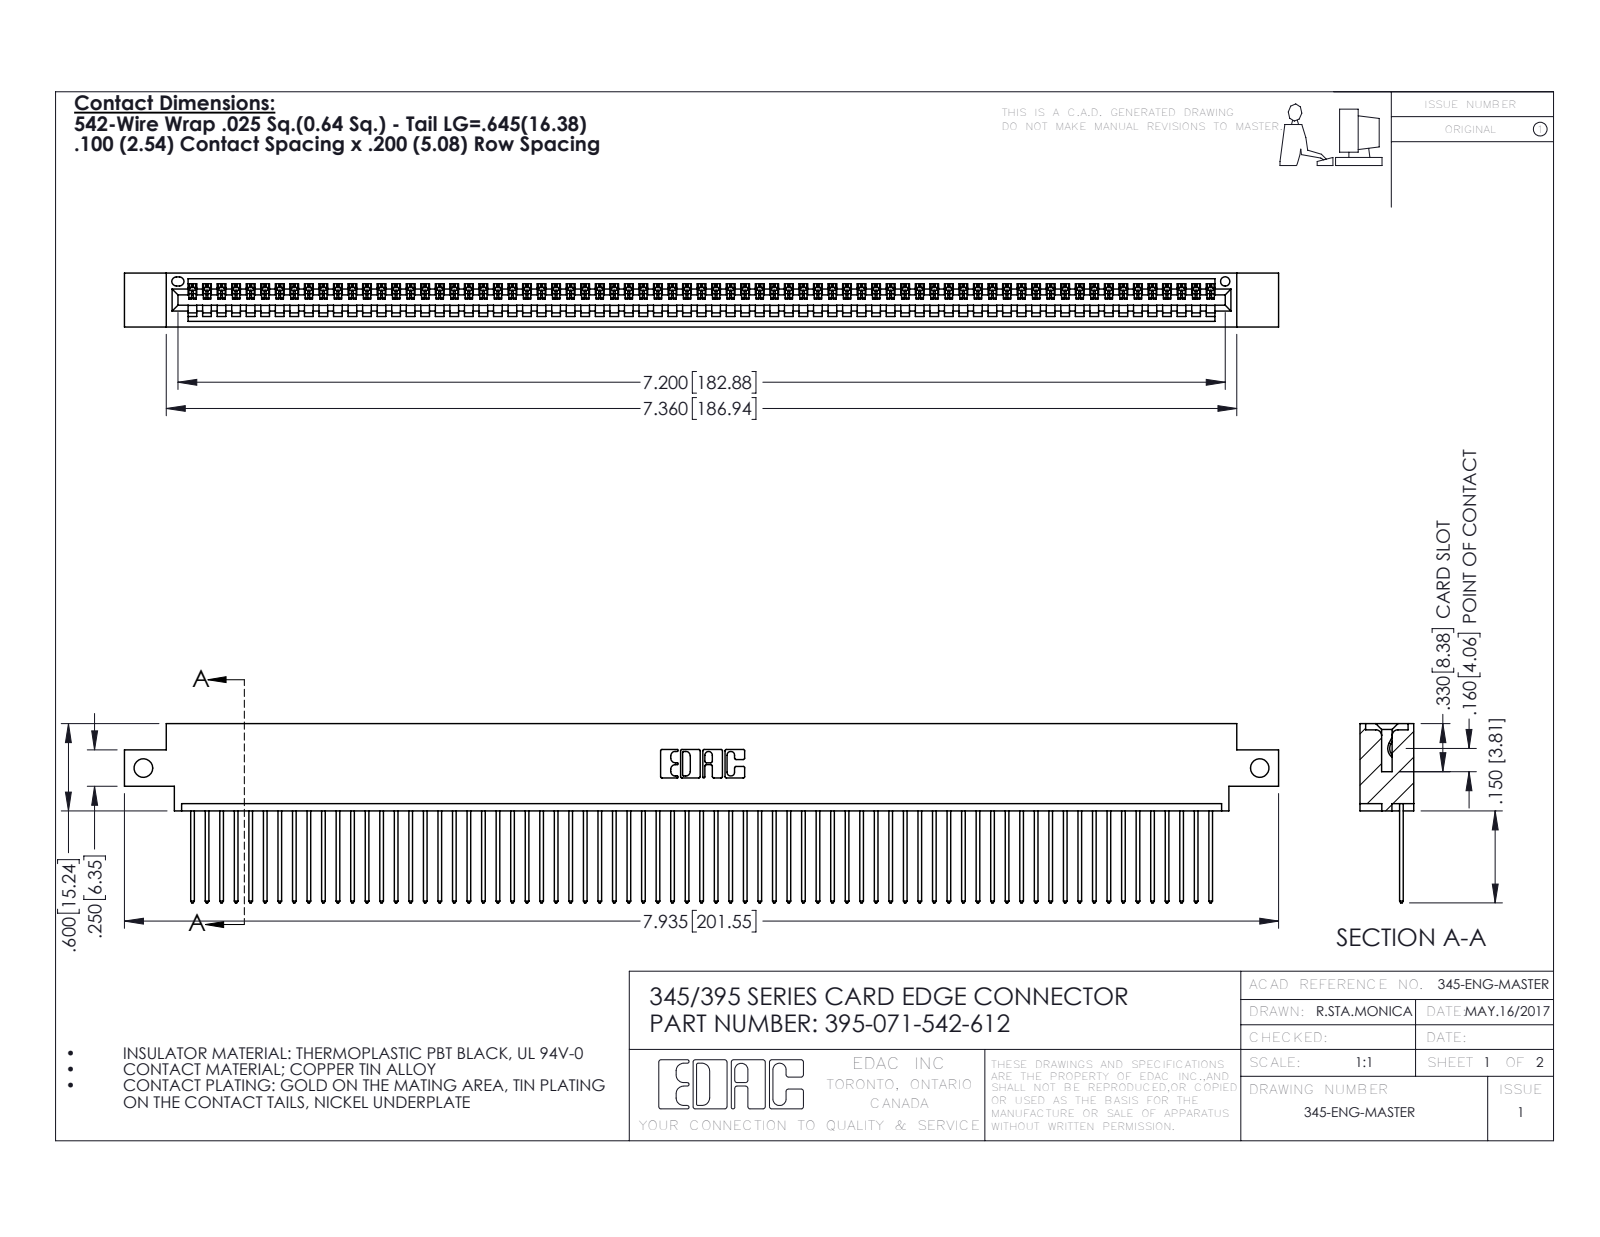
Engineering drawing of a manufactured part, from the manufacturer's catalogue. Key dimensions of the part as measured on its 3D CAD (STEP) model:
Part name (STEP PRODUCT): 345-292-001_345-293-142; 345 Part_0.170 Offset - Side Mount; 395-071-542-612
STEP written by: SolidWorks 2016 (CONFIG_CONTROL_DESIGN)
Units: inches
Bodies: 72 solids, 4248 faces (2924 planar, 1324 cylindrical, 0 other)
Overall size (bounding box): 7.935 × 1.232 × 0.37
Volume: 1.18 in³ · Surface area: 41.97 in²
Round holes (diameter × count): ⌀0.128 ×2, ⌀0.064 ×1
Partial cylindrical surfaces — rounded edges, fillets, slot ends (radius × count): R0.006 ×142, R0.01 ×142, R0.01 ×22, R0.007 ×6, R0.031 ×6, R0.026 ×3, R0.031 ×2, R0.04 ×2
Main face-to-face distances: 0.072, 0.298, 0.37, 0.098, 0.272, 0.025, 0.2, 0.225, 0.175, 0.149
Hole centre spacings: 7.675
